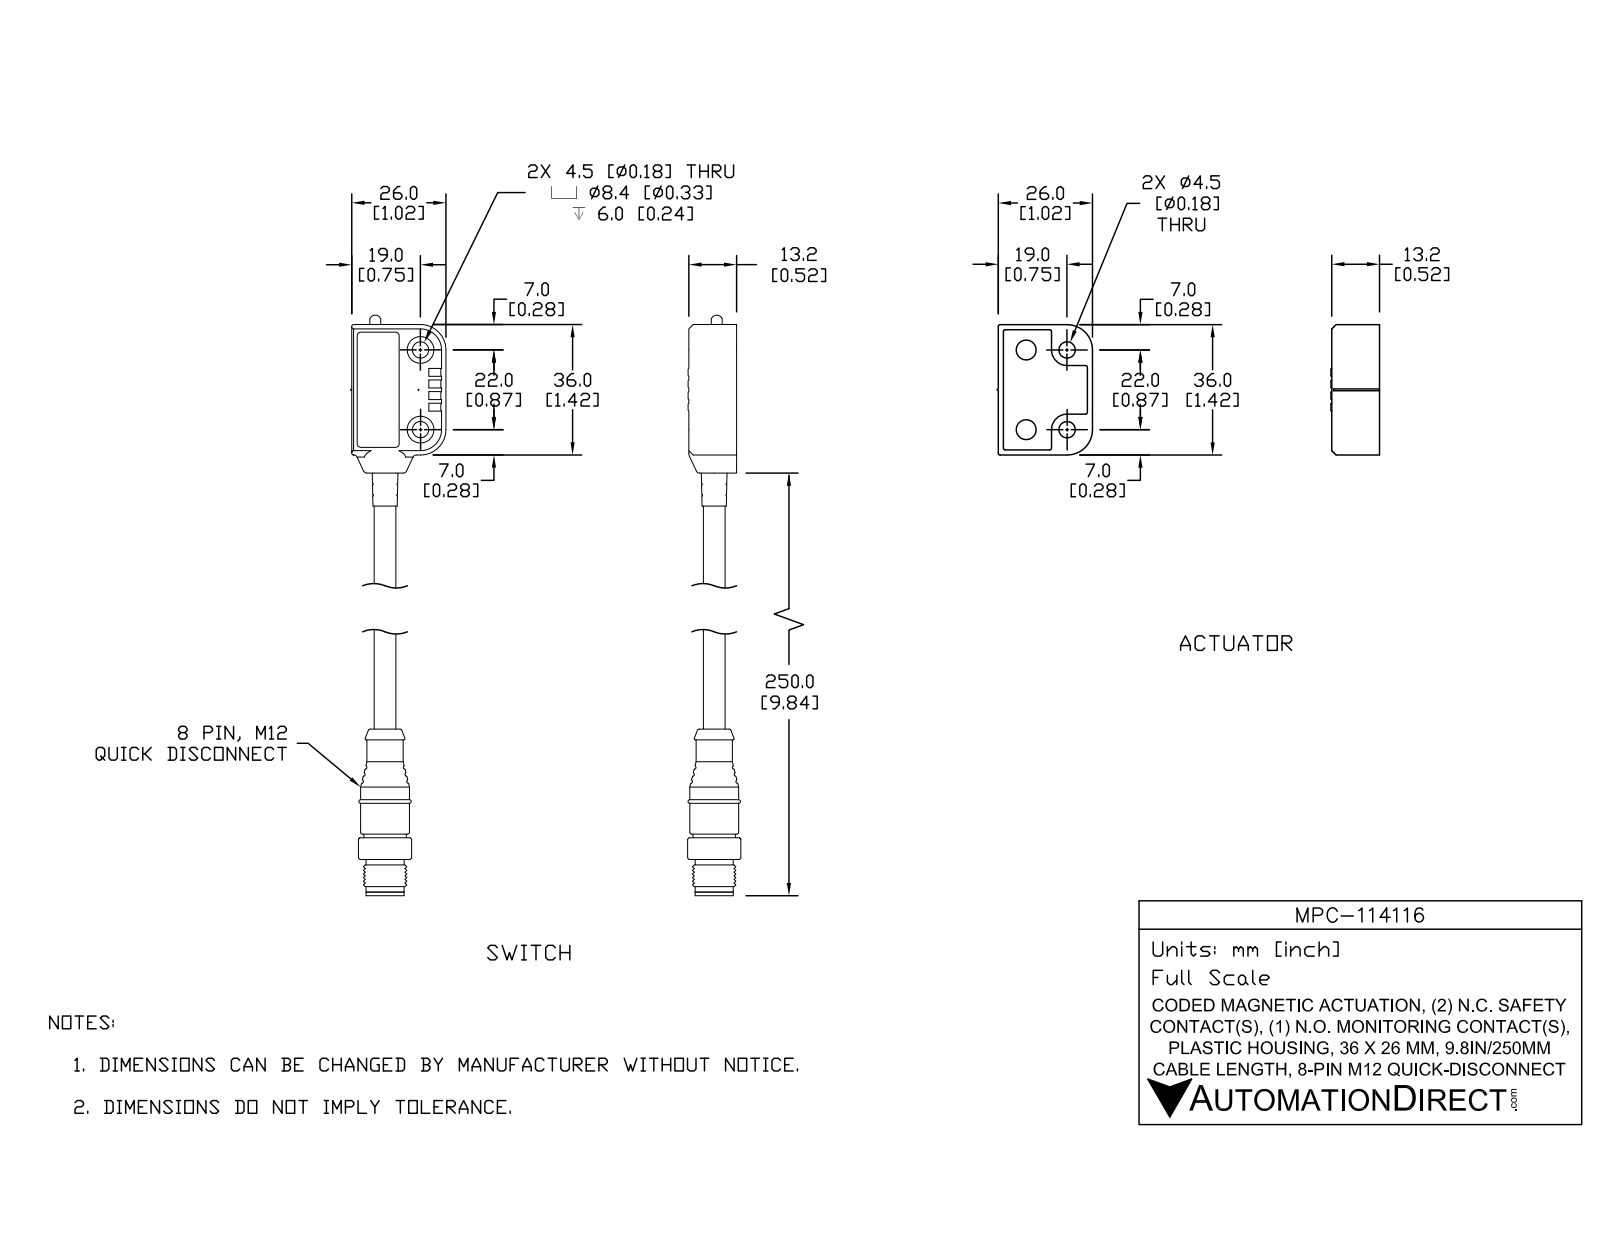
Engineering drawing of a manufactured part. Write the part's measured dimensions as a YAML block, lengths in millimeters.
part_name: "MPC-114116; MPC-114116_1; MPC-114116_2"
step_written_by: "SolidWorks 2017 (AUTOMOTIVE_DESIGN)"
units: millimeters
bodies: {solids: 11, faces: 1427, planar: 610, cylindrical: 460, other: 357}
overall_size: [293.6, 53, 14.7]
volume: 23710
surface_area: 23970
round_holes:
  - {diameter: 4.5, count: 4}
  - {diameter: 8.4, count: 4}
  - {diameter: 5, count: 2}
  - {diameter: 2.5, count: 1}
  - {diameter: 3, count: 1}
  - {diameter: 5, count: 1}
  - {diameter: 5.9, count: 1}
  - {diameter: 6.2, count: 1}
  - {diameter: 7.4, count: 1}
  - {diameter: 8.3, count: 1}
  - {diameter: 11.8, count: 1}
round_bosses_or_shafts:
  - {diameter: 0.8, count: 10}
  - {diameter: 6, count: 2}
  - {diameter: 5, count: 2}
  - {diameter: 2.3, count: 2}
  - {diameter: 2, count: 2}
  - {diameter: 13.5, count: 1}
  - {diameter: 11.7, count: 1}
  - {diameter: 10.5, count: 1}
partial_cylinders:
  - {radius: 0.5, count: 84}
  - {radius: 0.3, count: 32}
  - {radius: 0.2, count: 30}
  - {radius: 0.1, count: 17}
  - {radius: 1, count: 13}
  - {radius: 4.3, count: 4}
  - {radius: 5.1, count: 4}
  - {radius: 7, count: 4}
face_to_face_distances: [1.4, 12.9, 11.4, 11.7, 1.5, 1.2, 27, 12.6, 11.3, 0.8]
hole_center_spacings: [22, 11, 11.3, 24.7, 27.7, 29.3, 35.4, 39]
